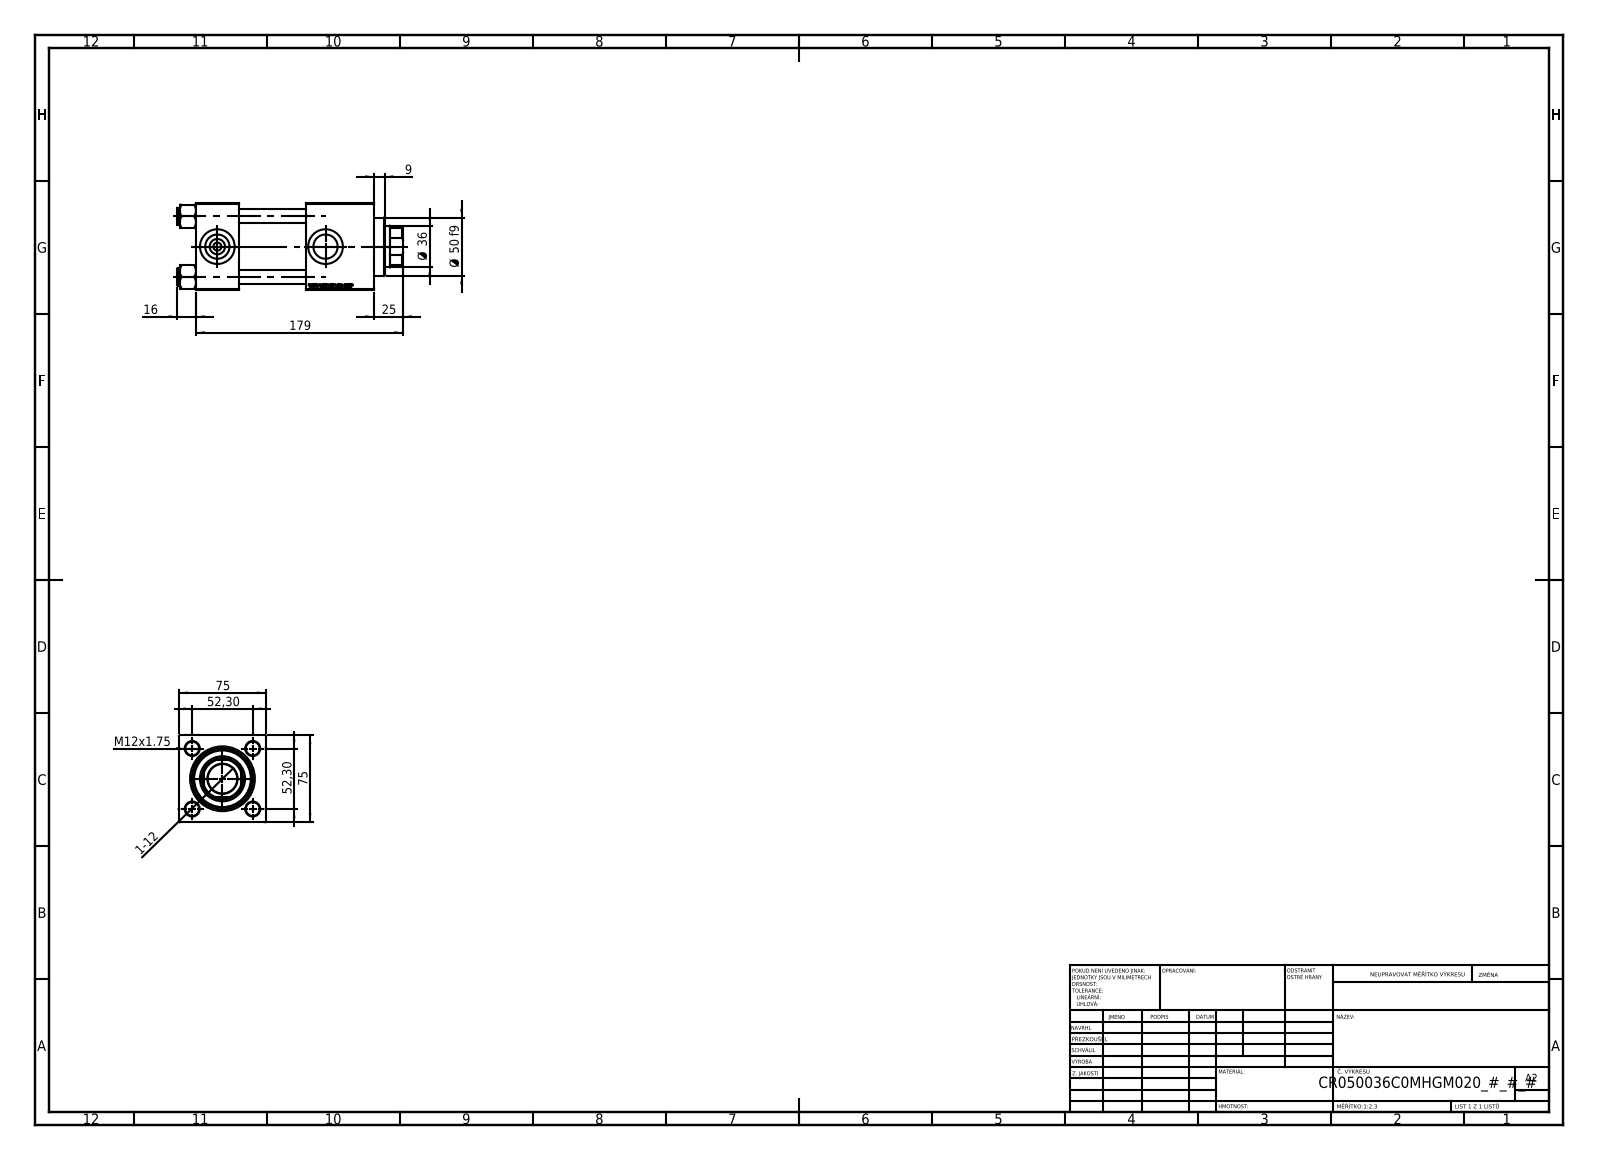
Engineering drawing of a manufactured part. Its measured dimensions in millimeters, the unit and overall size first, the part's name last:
Units: millimetres
Overall size (bounding box): 195 × 75.54 × 75
Round holes (diameter × count): ⌀12 ×4, ⌀7 ×2, ⌀20.96 ×2, ⌀30 ×2, ⌀25.5 ×1, ⌀36 ×1, ⌀39 ×1, ⌀41 ×1, ⌀53 ×1
Round bosses / shafts (diameter × count): ⌀15 ×4, ⌀56 ×1, ⌀50 ×1
Partial cylindrical surfaces — rounded edges, fillets, slot ends (radius × count): R17.5 ×1
Main face-to-face distances: 75, 37, 95, 58, 154, 117, 59, 125.3, 88.3, 30.3
Hole centre spacings: 36.98, 52.3, 73.96, 93.5
Volume: 686 044 mm³ · Surface area: 155 490 mm²
Bodies: 11 solids, 1148 faces (526 planar, 86 cylindrical, 536 other)
Part name (STEP PRODUCT): V215_VC_A; V215CR_C_TYCINKA; V215CR_VCP_C; NUT_M5_C (+1 more)
STEP written by: SolidWorks 2019 (CONFIG_CONTROL_DESIGN)
